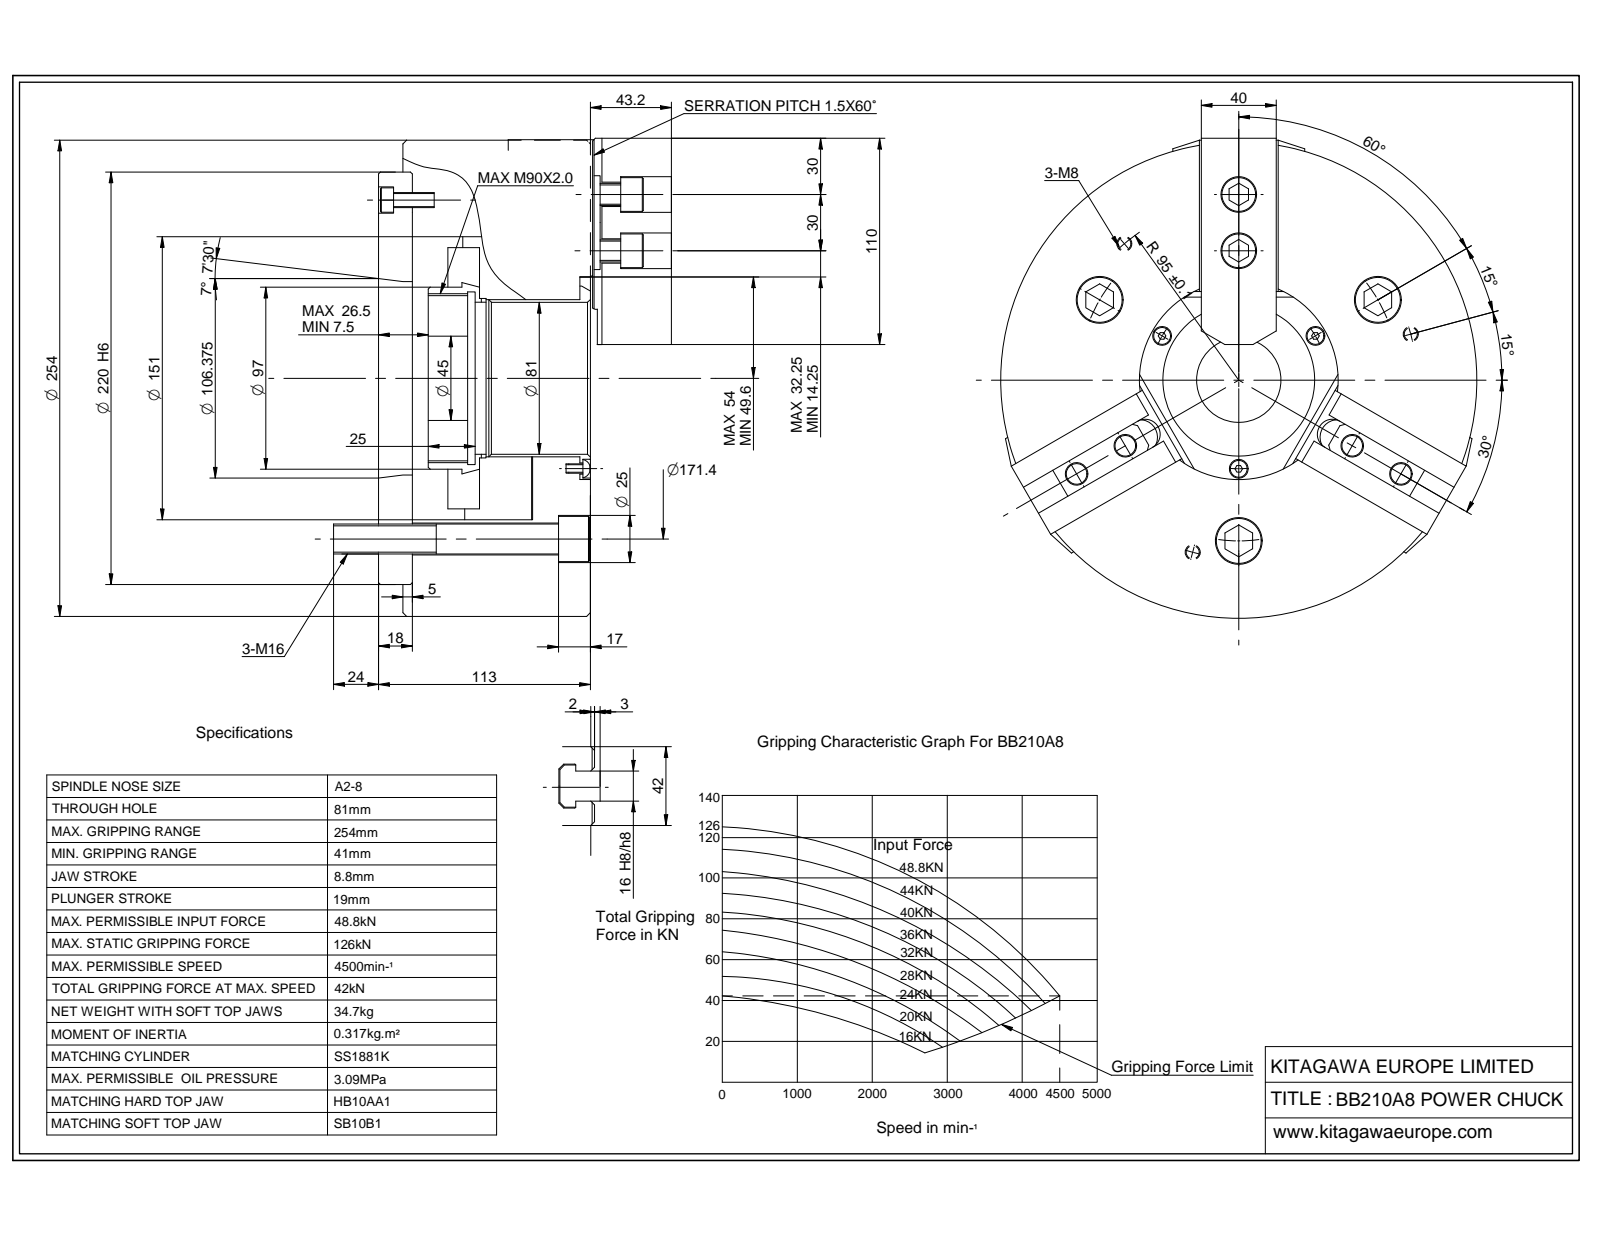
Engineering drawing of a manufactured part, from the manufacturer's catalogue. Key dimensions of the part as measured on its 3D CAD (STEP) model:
Part name (STEP PRODUCT): BB210A8 SOLID
STEP written by: ST-DEVELOPER v16.7 (AUTOMOTIVE_DESIGN)
Units: millimetres
Bodies: 1 solid, 3892 faces (3138 planar, 341 cylindrical, 413 other)
Overall size (bounding box): 273.25 × 272.71 × 180.2
Volume: 4 915 000 mm³ · Surface area: 544 120 mm²
Round holes (diameter × count): ⌀17 ×15, ⌀3.8 ×12, ⌀11 ×9, ⌀10 ×8, ⌀6 ×7, ⌀8.5 ×6, ⌀12 ×6, ⌀13 ×6, ⌀14 ×6, ⌀19 ×6, ⌀4.92 ×4, ⌀2 ×3
Round bosses / shafts (diameter × count): ⌀16 ×9, ⌀18 ×6, ⌀24 ×3, ⌀10.5 ×3, ⌀254 ×1, ⌀151 ×1, ⌀86 ×1
Partial cylindrical surfaces — rounded edges, fillets, slot ends (radius × count): R7 ×17, R0.4 ×12, R0.49 ×12, R0.6 ×12, R0.49 ×6, R0.56 ×6, R0.8 ×6, R1.2 ×6
Main face-to-face distances: 113, 28, 37, 10.5, 5, 13, 40, 100, 119.2, 156.2
Hole centre spacings: 85.72, 81.14, 23.7, 55.55, 62.5, 84.93, 85.5, 97.33
